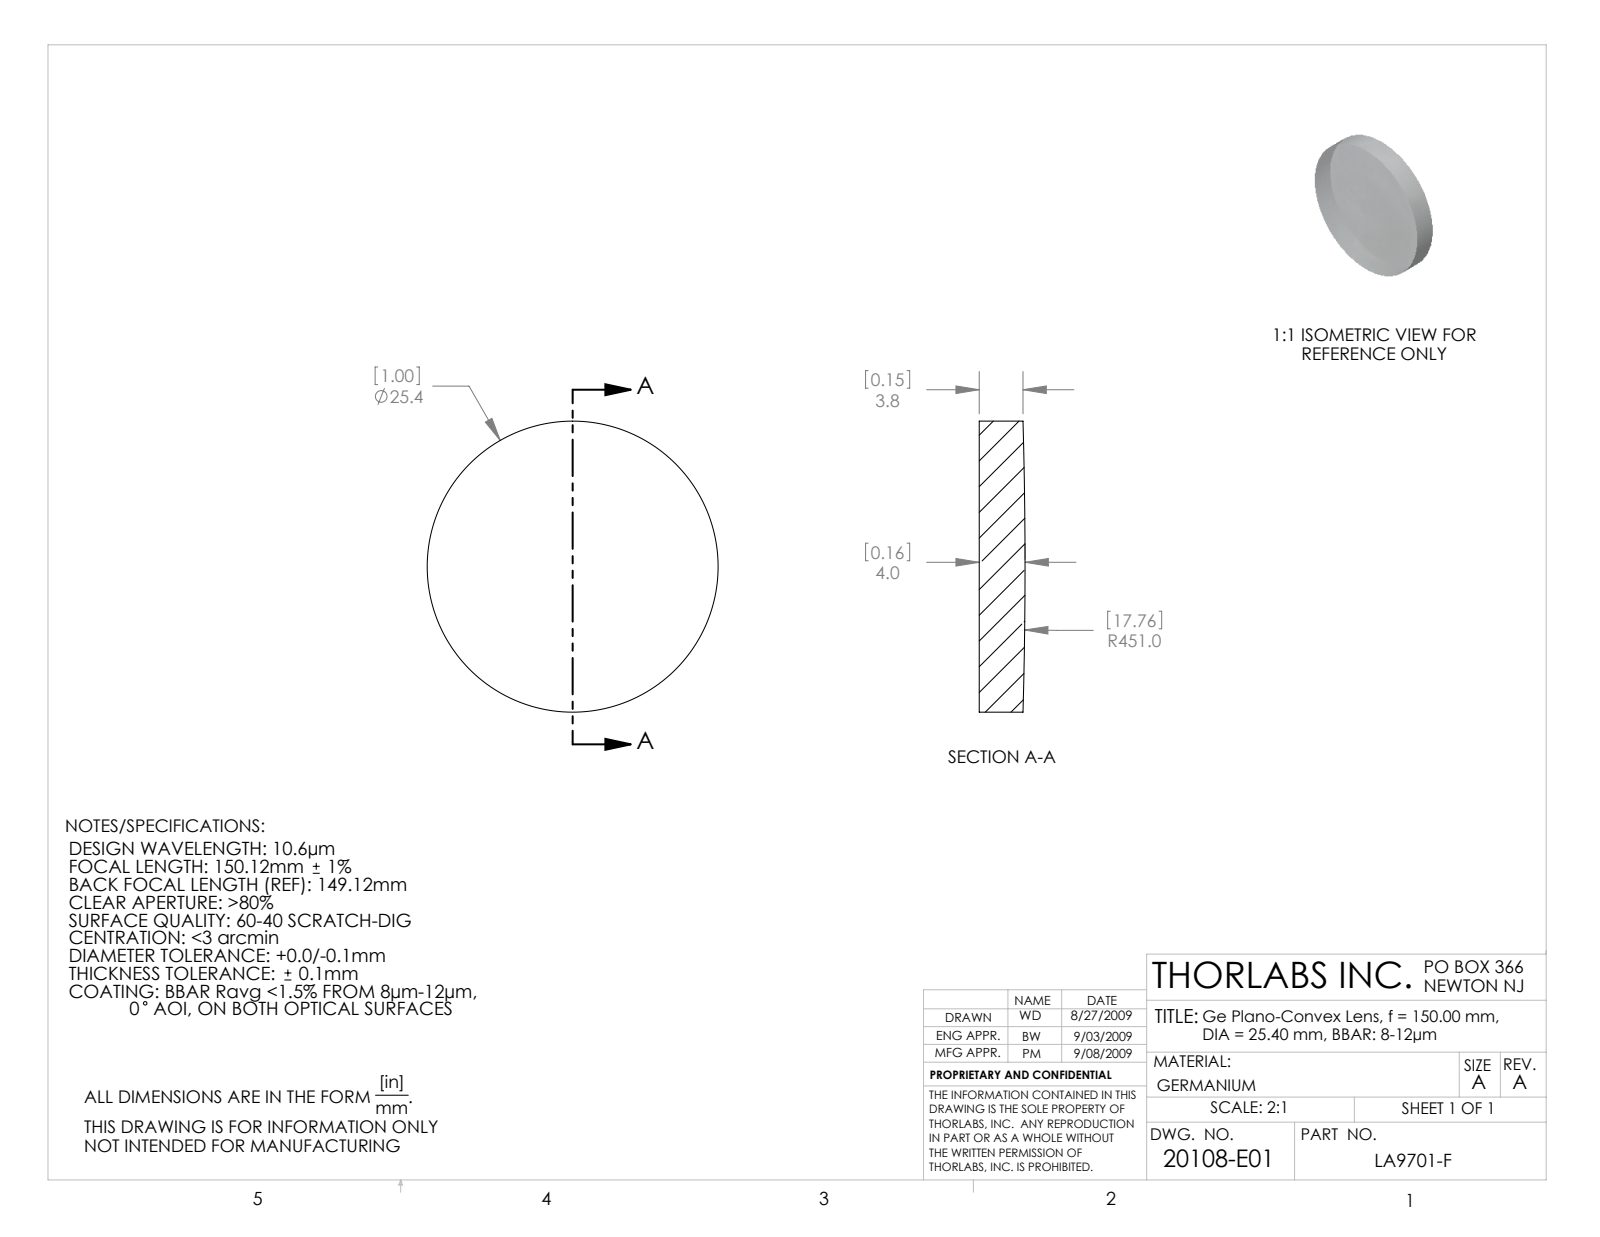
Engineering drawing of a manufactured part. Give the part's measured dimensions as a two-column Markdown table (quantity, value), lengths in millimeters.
| quantity | value |
| --- | --- |
| part name | 20108-E0W |
| STEP written by | SolidWorks 2007 (CONFIG_CONTROL_DESIGN) |
| units | millimeters |
| bodies | 1 solid, 5 faces (1 planar, 2 cylindrical, 2 other) |
| overall size | 25.4 × 25.4 × 4 |
| volume | 1 982 mm³ |
| surface area | 1 318 mm² |
| round bosses / shafts (diameter × count) | 25.4 × 1 |
